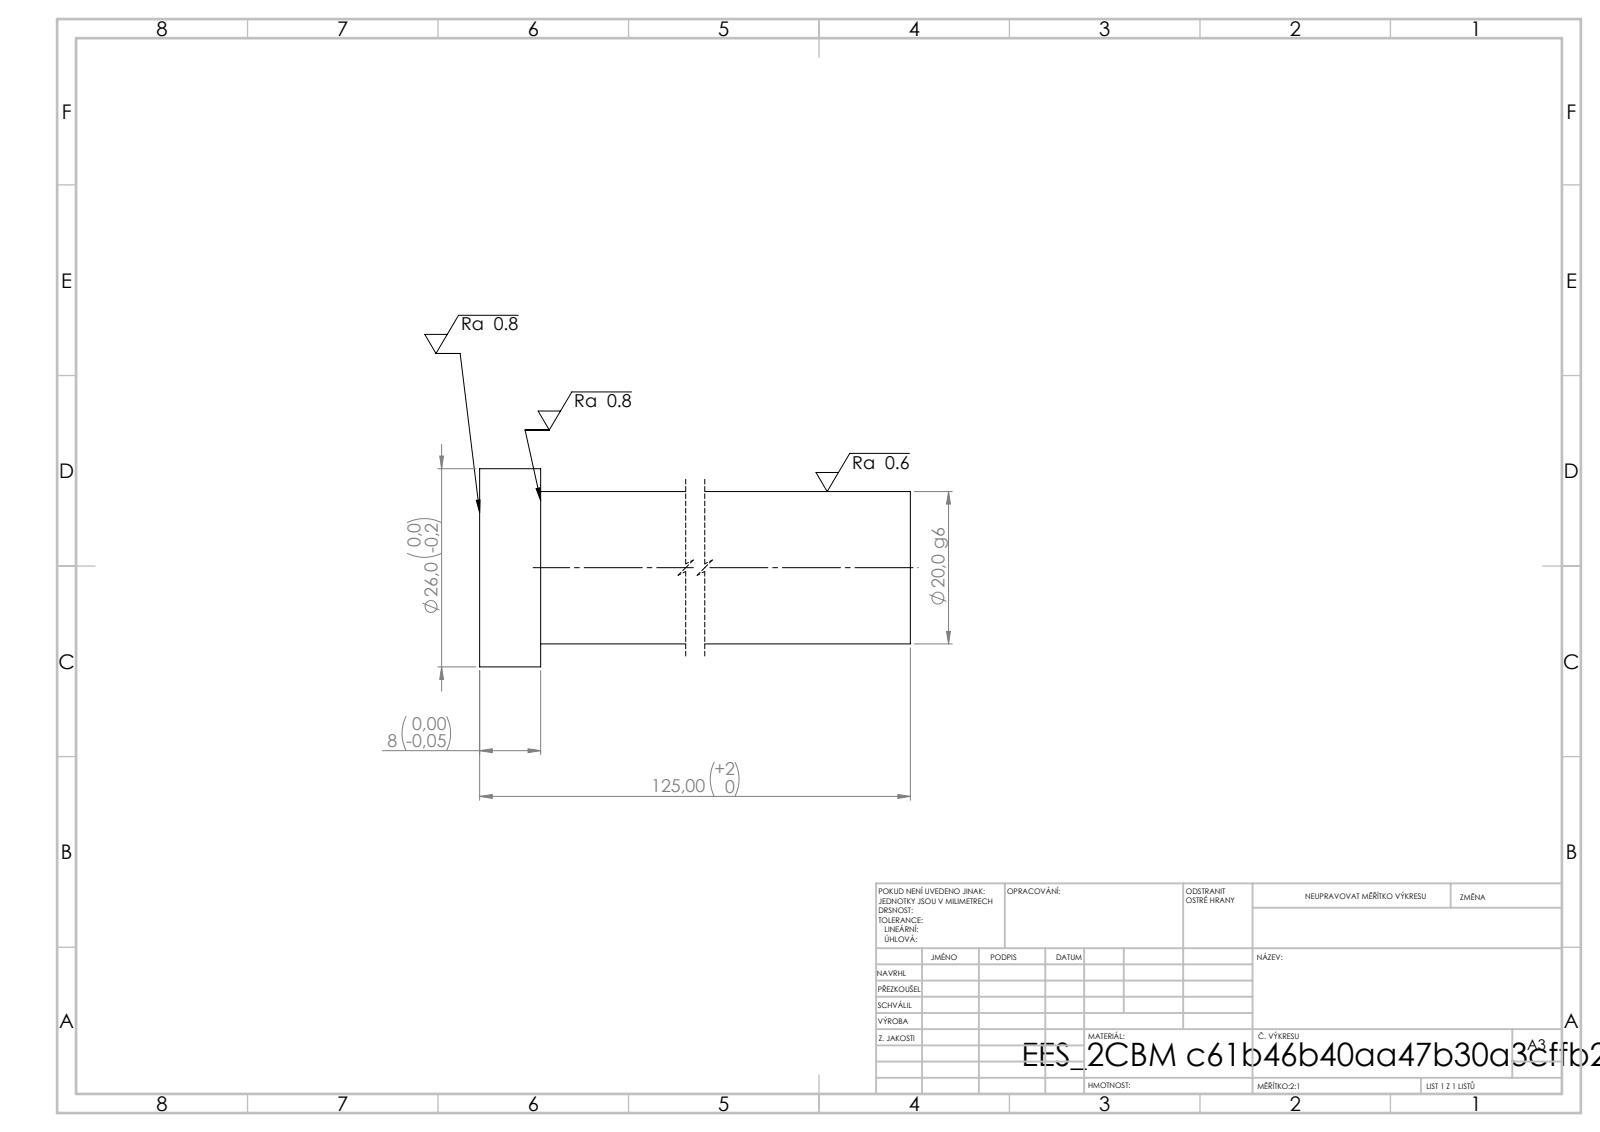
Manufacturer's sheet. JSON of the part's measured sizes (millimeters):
{"step_written_by": "SolidWorks 2019 (CONFIG_CONTROL_DESIGN)", "units": "millimeters", "bodies": {"solids": 1, "faces": 7, "planar": 3, "cylindrical": 4, "other": 0}, "overall_size": [125, 26, 26], "volume_mm3": 41004, "surface_area_mm2": 9067, "round_bosses_or_shafts": [[26, 1], [20, 1]], "face_to_face_distances": [125, 8, 117]}
